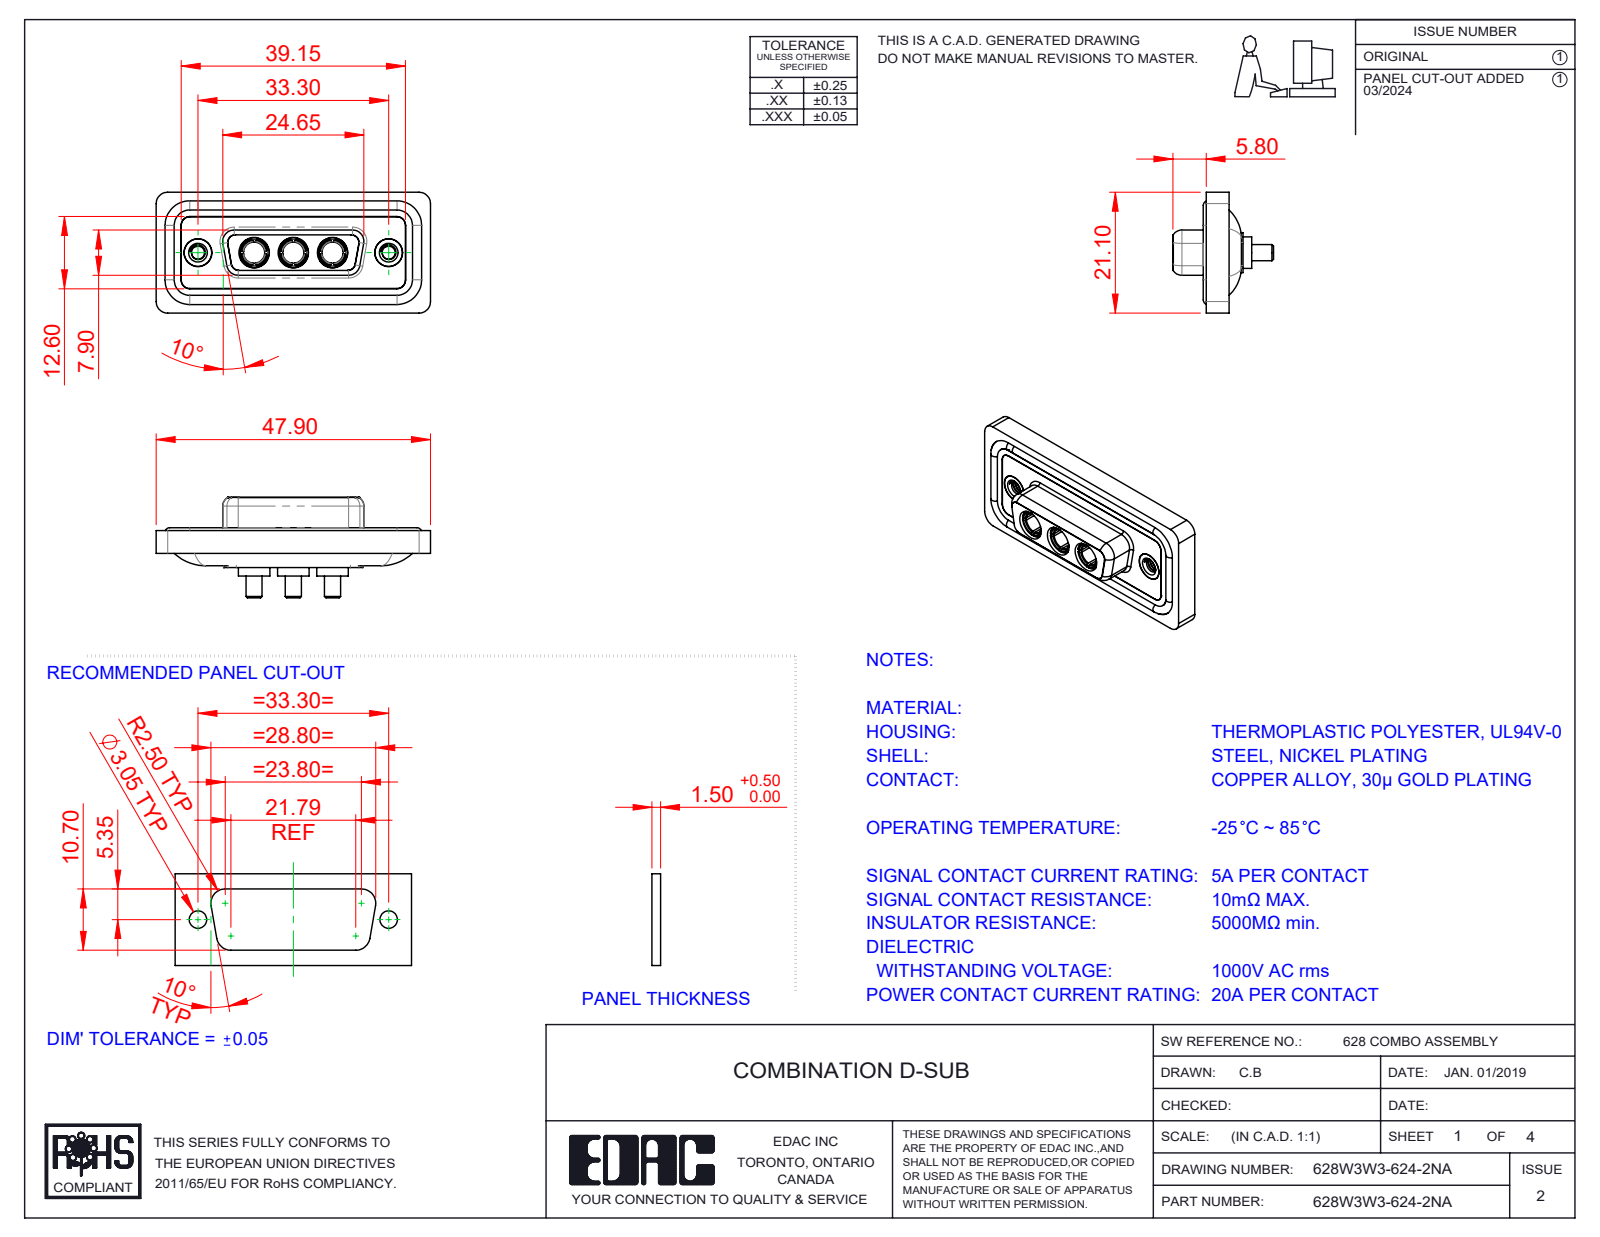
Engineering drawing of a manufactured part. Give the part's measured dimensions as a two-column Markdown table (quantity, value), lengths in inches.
| quantity | value |
| --- | --- |
| part name | 628Combo Waterproof Housing_15 Contacts; 628Combo Housing_3W3; 628Combo Shell Rear_15 Contacts; Power Socket_20A S (+3 more) |
| STEP written by | SolidWorks 2023 (CONFIG_CONTROL_DESIGN) |
| units | inches |
| bodies | 13 solids, 606 faces (192 planar, 259 cylindrical, 155 other) |
| overall size | 1.886 × 0.831 × 0.691 |
| volume | 0.368 in³ |
| surface area | 15.09 in² |
| round holes (diameter × count) | 0.191 × 5, 0.146 × 3, 0.209 × 3, 0.089 × 2, 0.157 × 2, 0.159 × 2, 0.197 × 2 |
| round bosses / shafts (diameter × count) | 0.063 × 4, 0.217 × 3, 0.205 × 3, 0.195 × 3, 0.187 × 3, 0.148 × 3, 0.11 × 3, 0.195 × 2 |
| partial cylindrical surfaces (radius × count) | 0.059 × 22, 0.079 × 20, 0.053 × 12, 0.063 × 8, 0.01 × 4, 0.02 × 4, 0.024 × 4, 0.026 × 4 |
| main face-to-face distances | 0.016, 0.071, 0.063, 0.02, 0.293, 0.043, 0.114, 0.222, 0.278, 0.26 |
| hole center spacings | 0.27, 0.386, 0.656, 0.925, 0.539, 1.311 |
